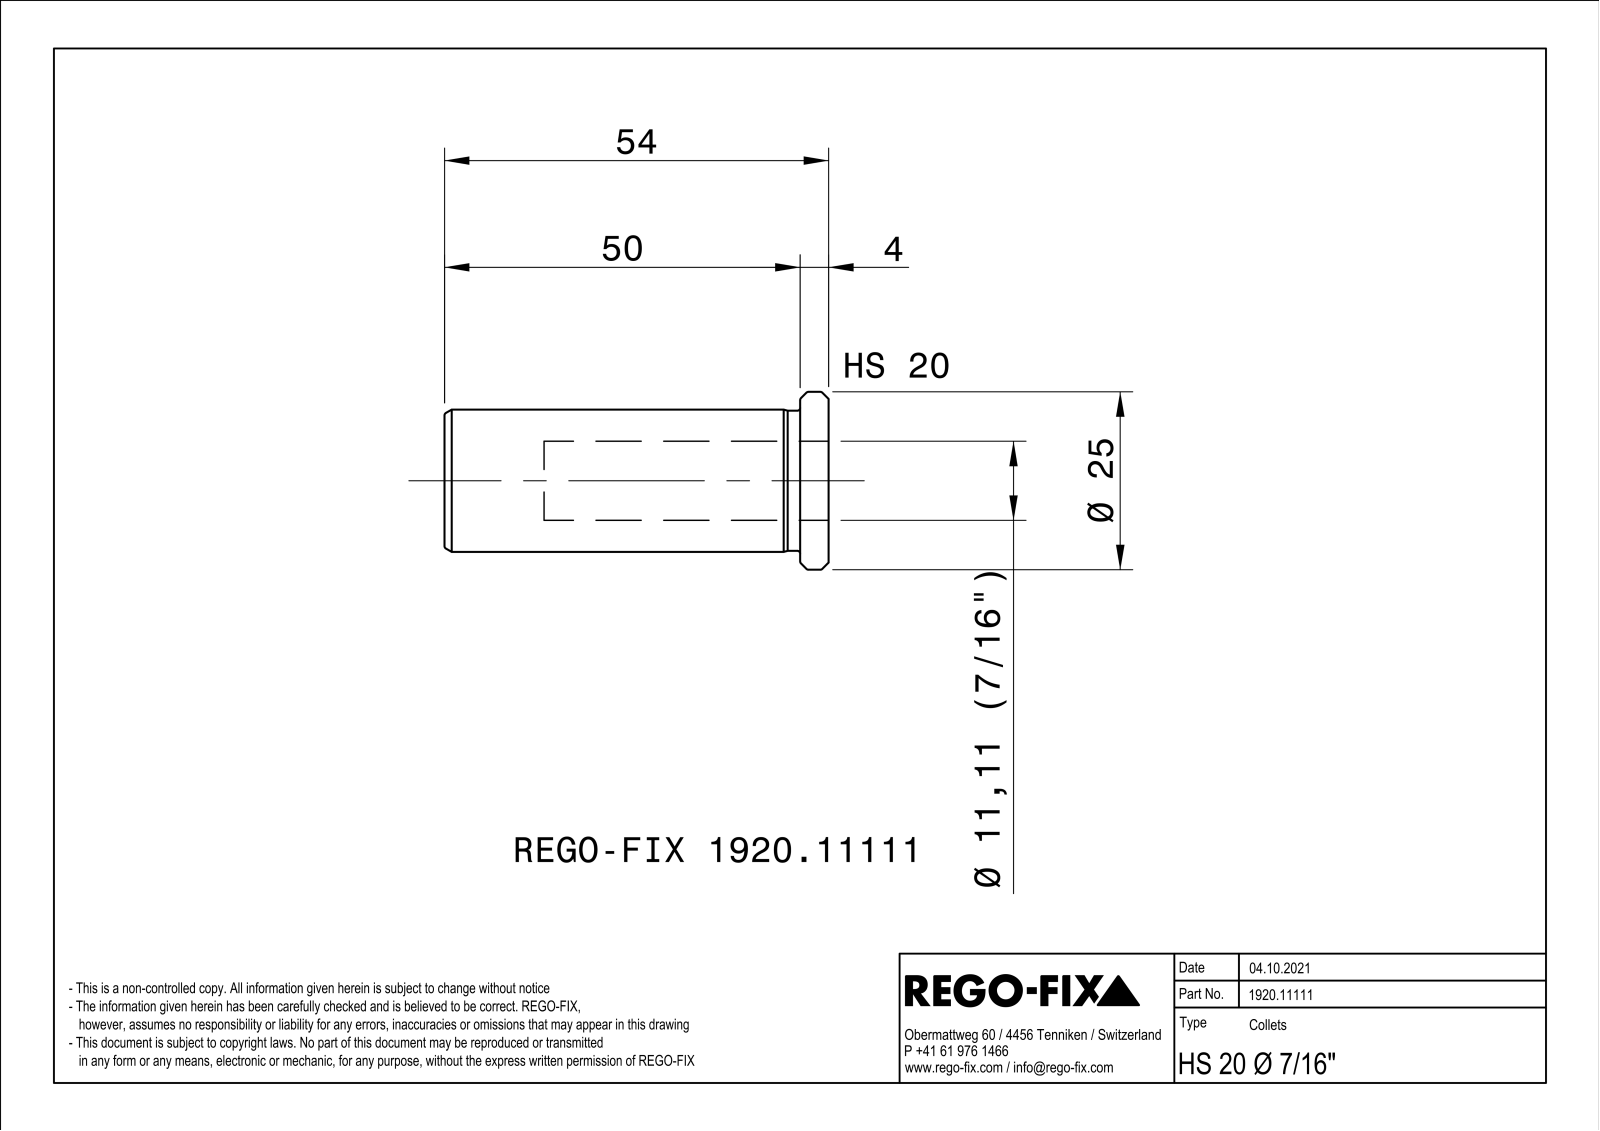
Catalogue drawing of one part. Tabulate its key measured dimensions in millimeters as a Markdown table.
| quantity | value |
| --- | --- |
| part name | NOCUT |
| STEP written by | SIEMENS PLM Software Solid Edge ST10 (AUTOMOTIVE_DESIGN) |
| units | millimeters |
| bodies | 1 solid, 70 faces (22 planar, 11 cylindrical, 37 other) |
| overall size | 54 × 24.98 × 24.98 |
| volume | 10 328 mm³ |
| surface area | 7 197 mm² |
| round holes (diameter × count) | 11.11 × 1, 16.5 × 1 |
| round bosses / shafts (diameter × count) | 25 × 1, 20 × 1, 19.7 × 1 |
| main face-to-face distances | 1, 4, 54, 50 |
